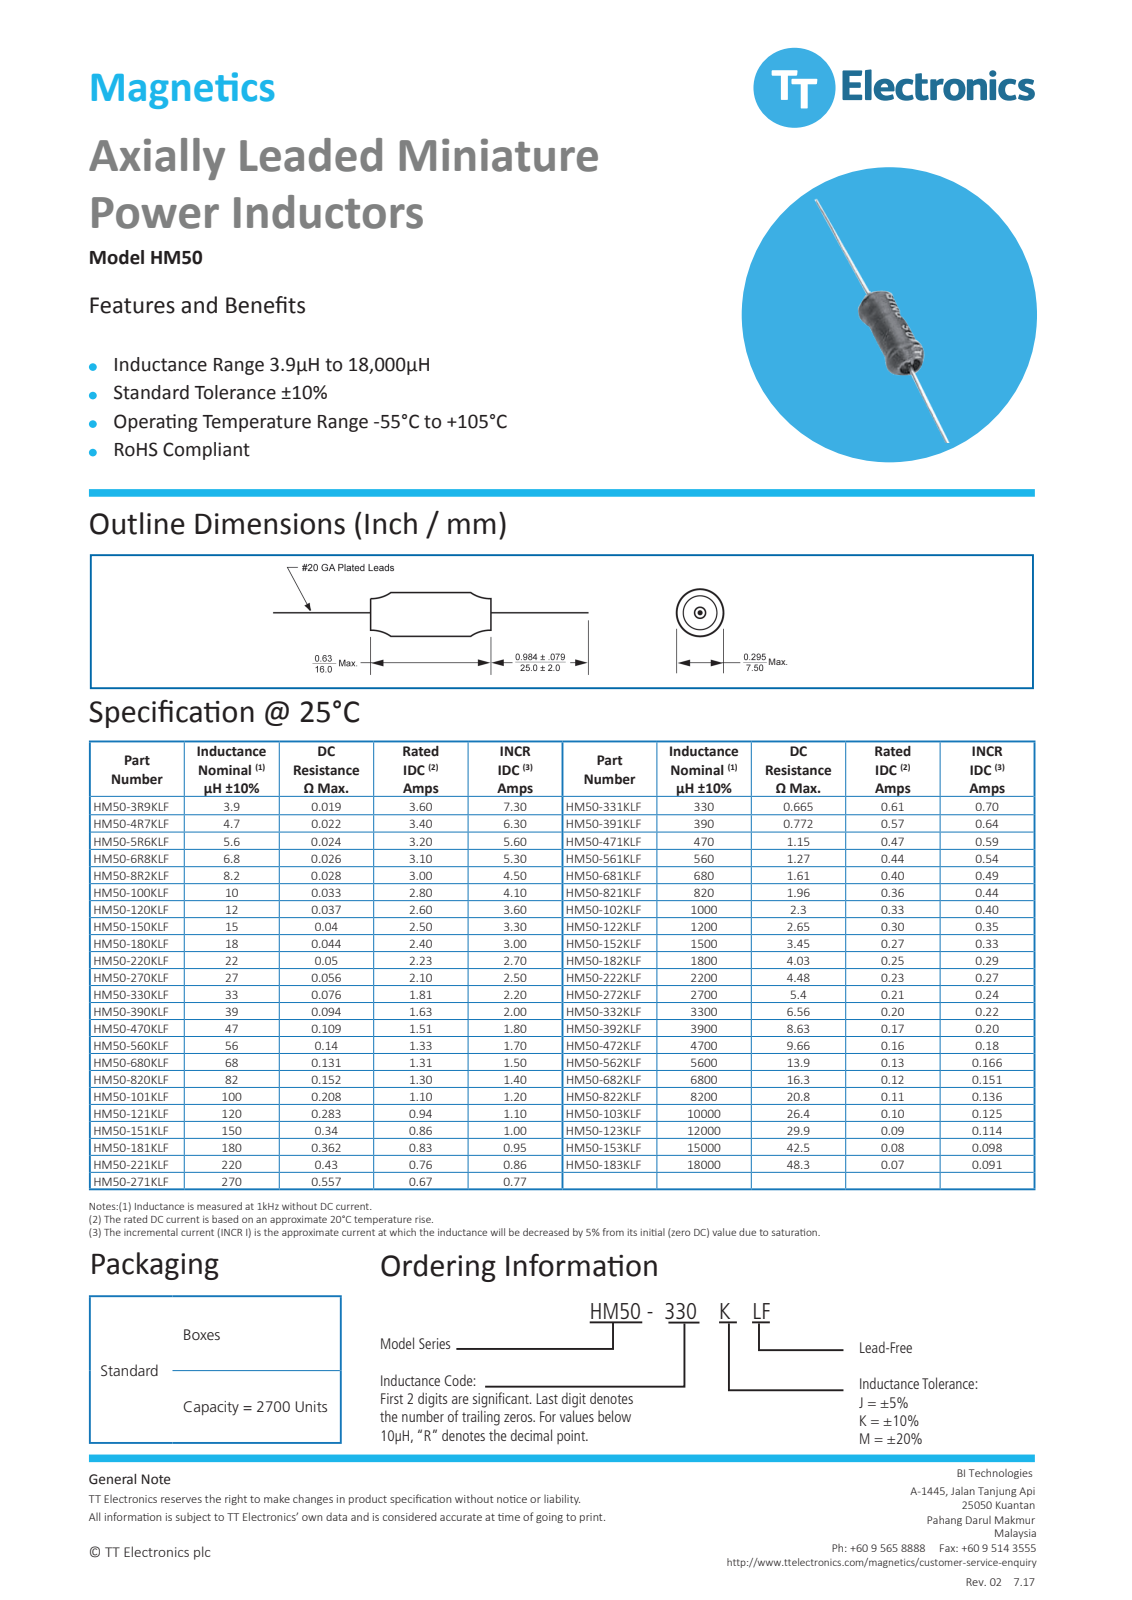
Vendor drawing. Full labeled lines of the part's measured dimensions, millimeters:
Part name (STEP PRODUCT): HM50
STEP written by: Solid Edge (AUTOMOTIVE_DESIGN)
Units: millimetres
Bodies: 1 solid, 17 faces (8 planar, 7 cylindrical, 2 other)
Overall size (bounding box): 66 × 7.51 × 7.51
Volume: 624 mm³ · Surface area: 598 mm²
Round holes (diameter × count): ⌀4.5 ×1
Round bosses / shafts (diameter × count): ⌀7.25 ×1, ⌀1 ×1, ⌀0.81 ×1
Main face-to-face distances: 13, 1.5, 14.5, 16, 25, 26.5, 39.5, 41, 66
